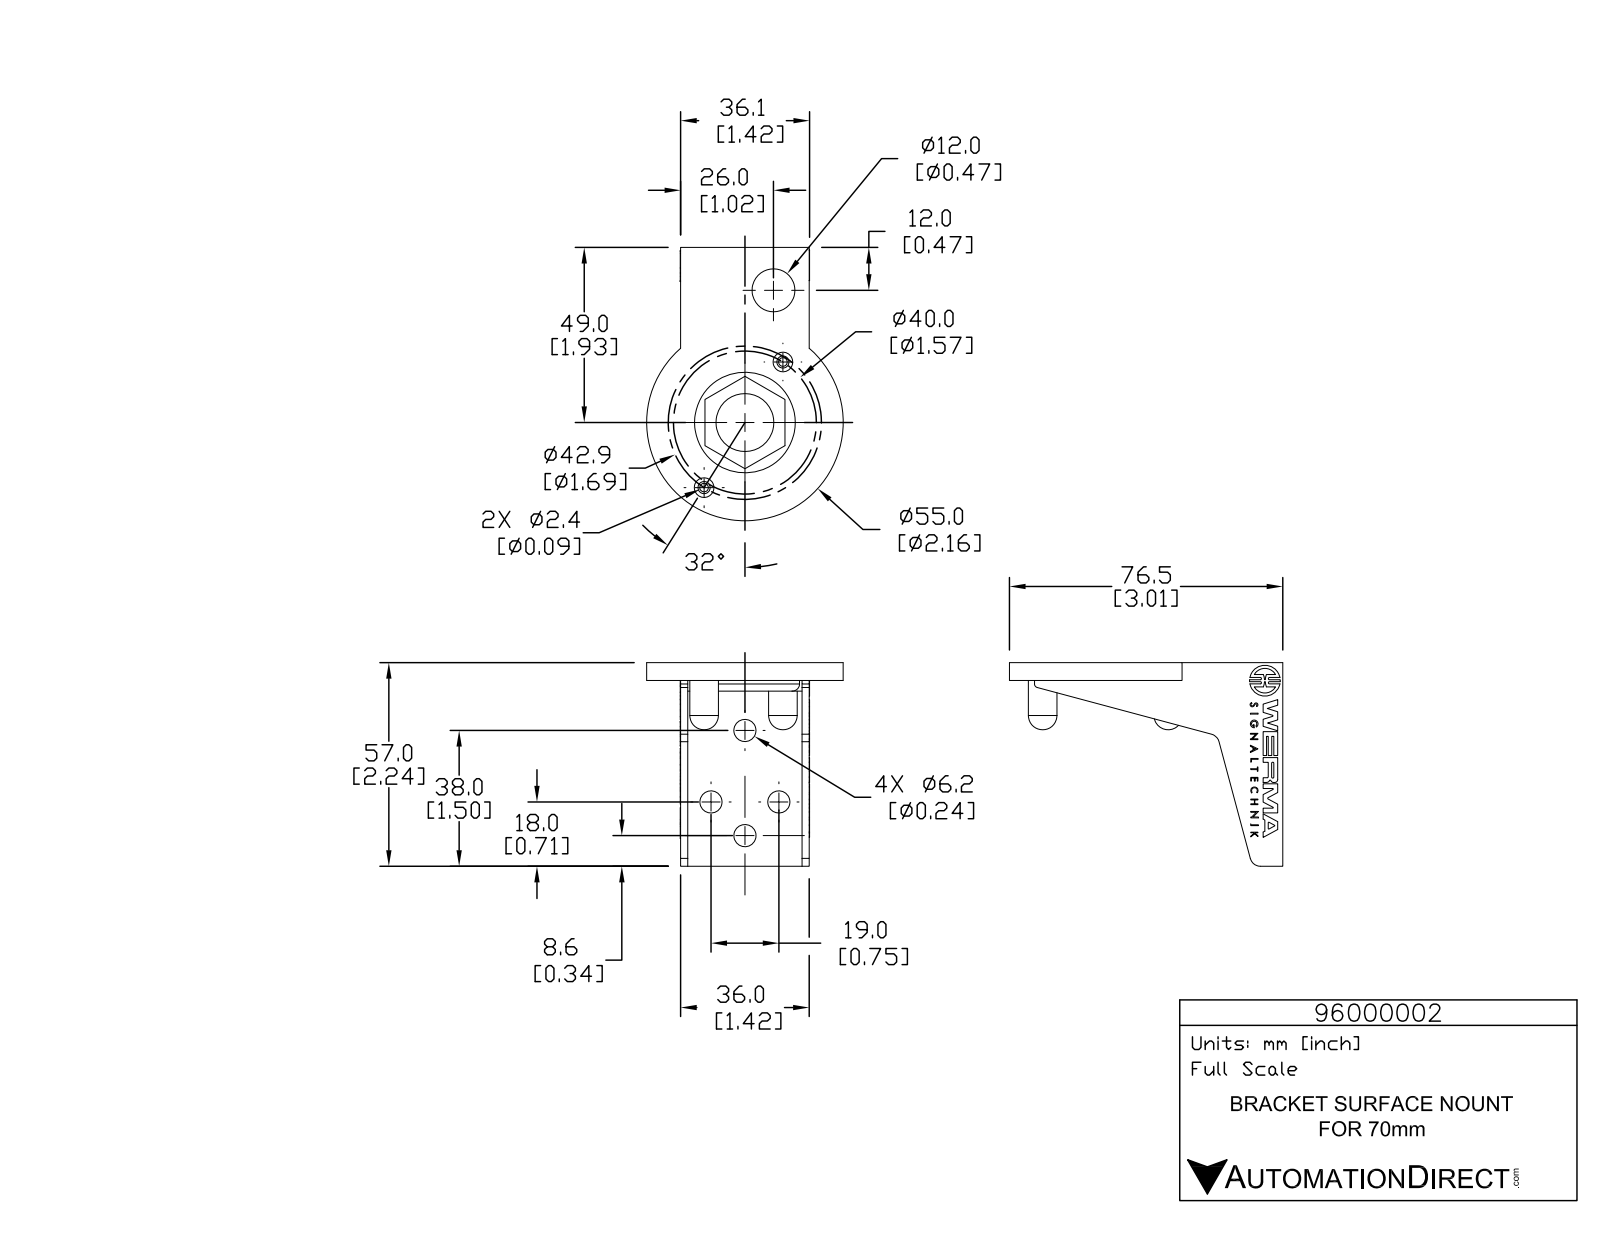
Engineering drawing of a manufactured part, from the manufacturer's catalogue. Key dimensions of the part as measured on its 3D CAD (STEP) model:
Part name (STEP PRODUCT): 96000002
STEP written by: SolidWorks 2015 (AUTOMOTIVE_DESIGN)
Units: inches
Bodies: 1 solid, 649 faces (469 planar, 167 cylindrical, 13 other)
Overall size (bounding box): 3.012 × 2.244 × 2.165
Volume: 1.168 in³ · Surface area: 29.57 in²
Round holes (diameter × count): ⌀0.244 ×4, ⌀0.059 ×2, ⌀0.134 ×2, ⌀0.217 ×2, ⌀0.315 ×1, ⌀0.472 ×1, ⌀0.638 ×1, ⌀1.109 ×1
Round bosses / shafts (diameter × count): ⌀0.339 ×2, ⌀0.315 ×2, ⌀0.084 ×2, ⌀0.472 ×1
Partial cylindrical surfaces — rounded edges, fillets, slot ends (radius × count): R0.005 ×6, R0.005 ×4, R0.012 ×4, R0.012 ×4, R0.012 ×4, R0.196 ×4, R0.236 ×3, R0.005 ×2
Main face-to-face distances: 0.079, 1.339, 1.417, 1.26, 0.157, 0.236, 0.118, 0.315, 0.039, 0.197
Hole centre spacings: 0.872, 0.526, 0.527, 0.618, 0.748, 0.787, 0.796, 0.846
